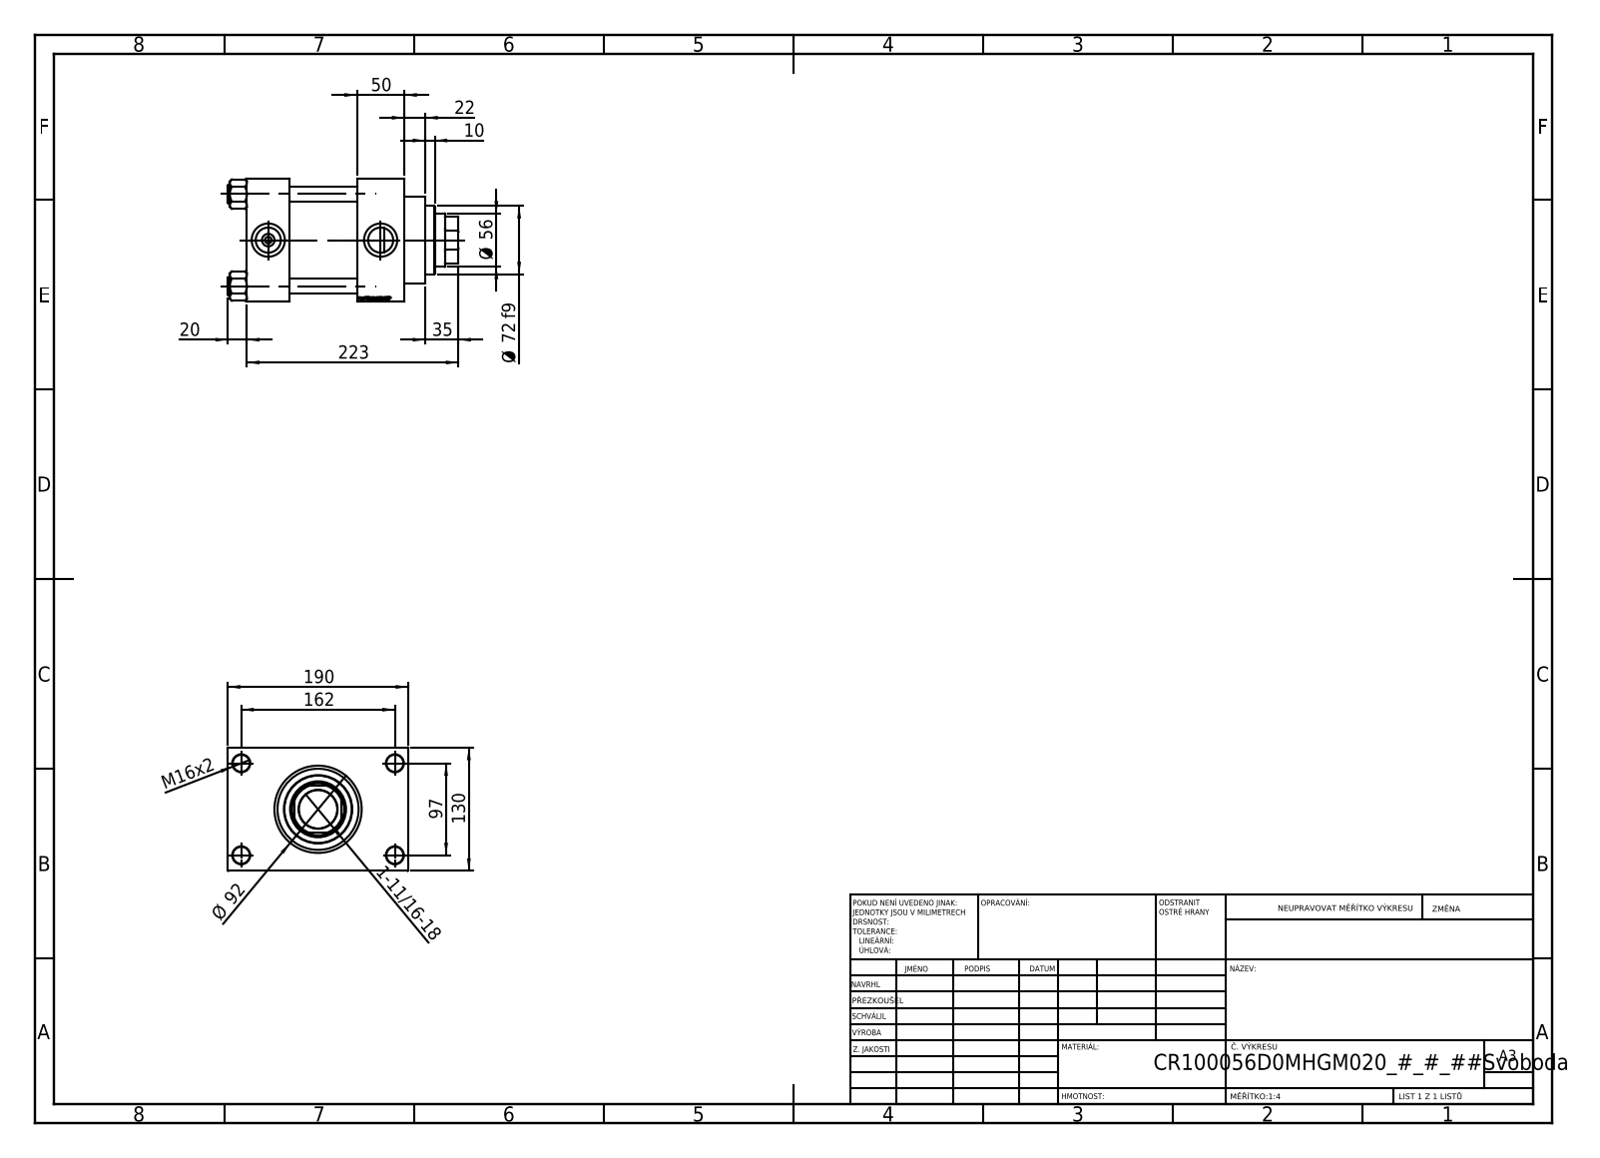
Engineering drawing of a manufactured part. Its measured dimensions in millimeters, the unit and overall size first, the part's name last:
Units: millimetres
Overall size (bounding box): 243 × 190 × 130
Round holes (diameter × count): ⌀16 ×4, ⌀18 ×4, ⌀7 ×2, ⌀26.44 ×2, ⌀35 ×2, ⌀40.5 ×1, ⌀56 ×1, ⌀59 ×1, ⌀76 ×1, ⌀85.5 ×1, ⌀100 ×1
Round bosses / shafts (diameter × count): ⌀19 ×4, ⌀106 ×1, ⌀92 ×1, ⌀72 ×1
Partial cylindrical surfaces — rounded edges, fillets, slot ends (radius × count): R27 ×1
Main face-to-face distances: 130, 116, 50, 45, 71, 121, 166, 30, 160, 20
Hole centre spacings: 32.55, 68.52, 94.41, 96.9, 102.27, 129.45, 161.73, 97
Volume: 2 628 000 mm³ · Surface area: 362 363 mm²
Bodies: 11 solids, 1151 faces (545 planar, 88 cylindrical, 518 other)
Part name (STEP PRODUCT): V215CR_D_Body; V215_VC_A; NUT_M5_D; V215CR_D_TYCINKA (+1 more)
STEP written by: SolidWorks 2019 (CONFIG_CONTROL_DESIGN)
